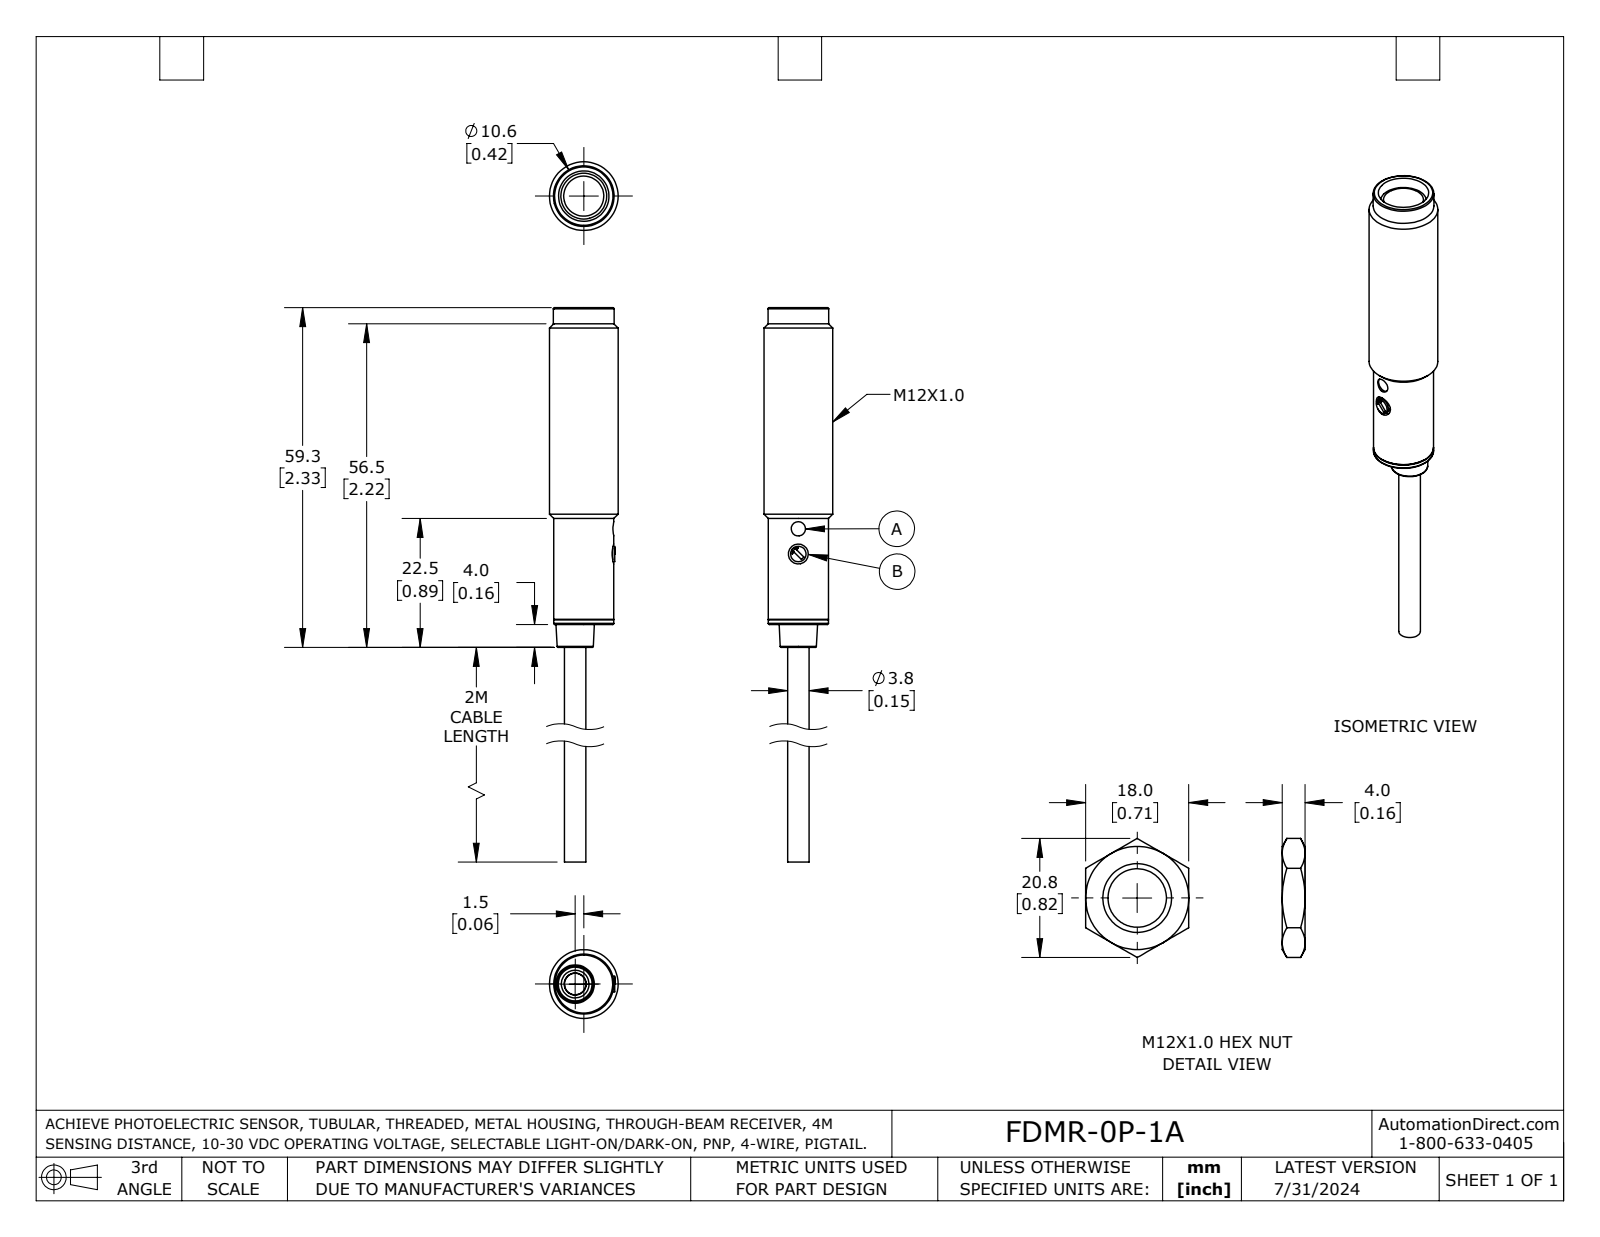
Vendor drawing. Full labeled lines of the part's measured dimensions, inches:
Part name (STEP PRODUCT): DME_1A_fig
STEP written by: SolidWorks 2023 (AUTOMOTIVE_DESIGN)
Units: inches
Bodies: 1 solid, 48 faces (25 planar, 13 cylindrical, 10 other)
Overall size (bounding box): 3.72 × 0.472 × 0.472
Volume: 0.373 in³ · Surface area: 4.434 in²
Round holes (diameter × count): ⌀0.098 ×1, ⌀0.118 ×1, ⌀0.138 ×1, ⌀0.152 ×1
Round bosses / shafts (diameter × count): ⌀0.472 ×1, ⌀0.417 ×1, ⌀0.413 ×1, ⌀0.276 ×1, ⌀0.148 ×1, ⌀0.106 ×1, ⌀0.098 ×1
Main face-to-face distances: 2.177, 2.11, 0.067, 1.543, 3.654, 3.72, 0.02, 1.386, 0.157, 2.268
Hole centre spacings: 0.173
